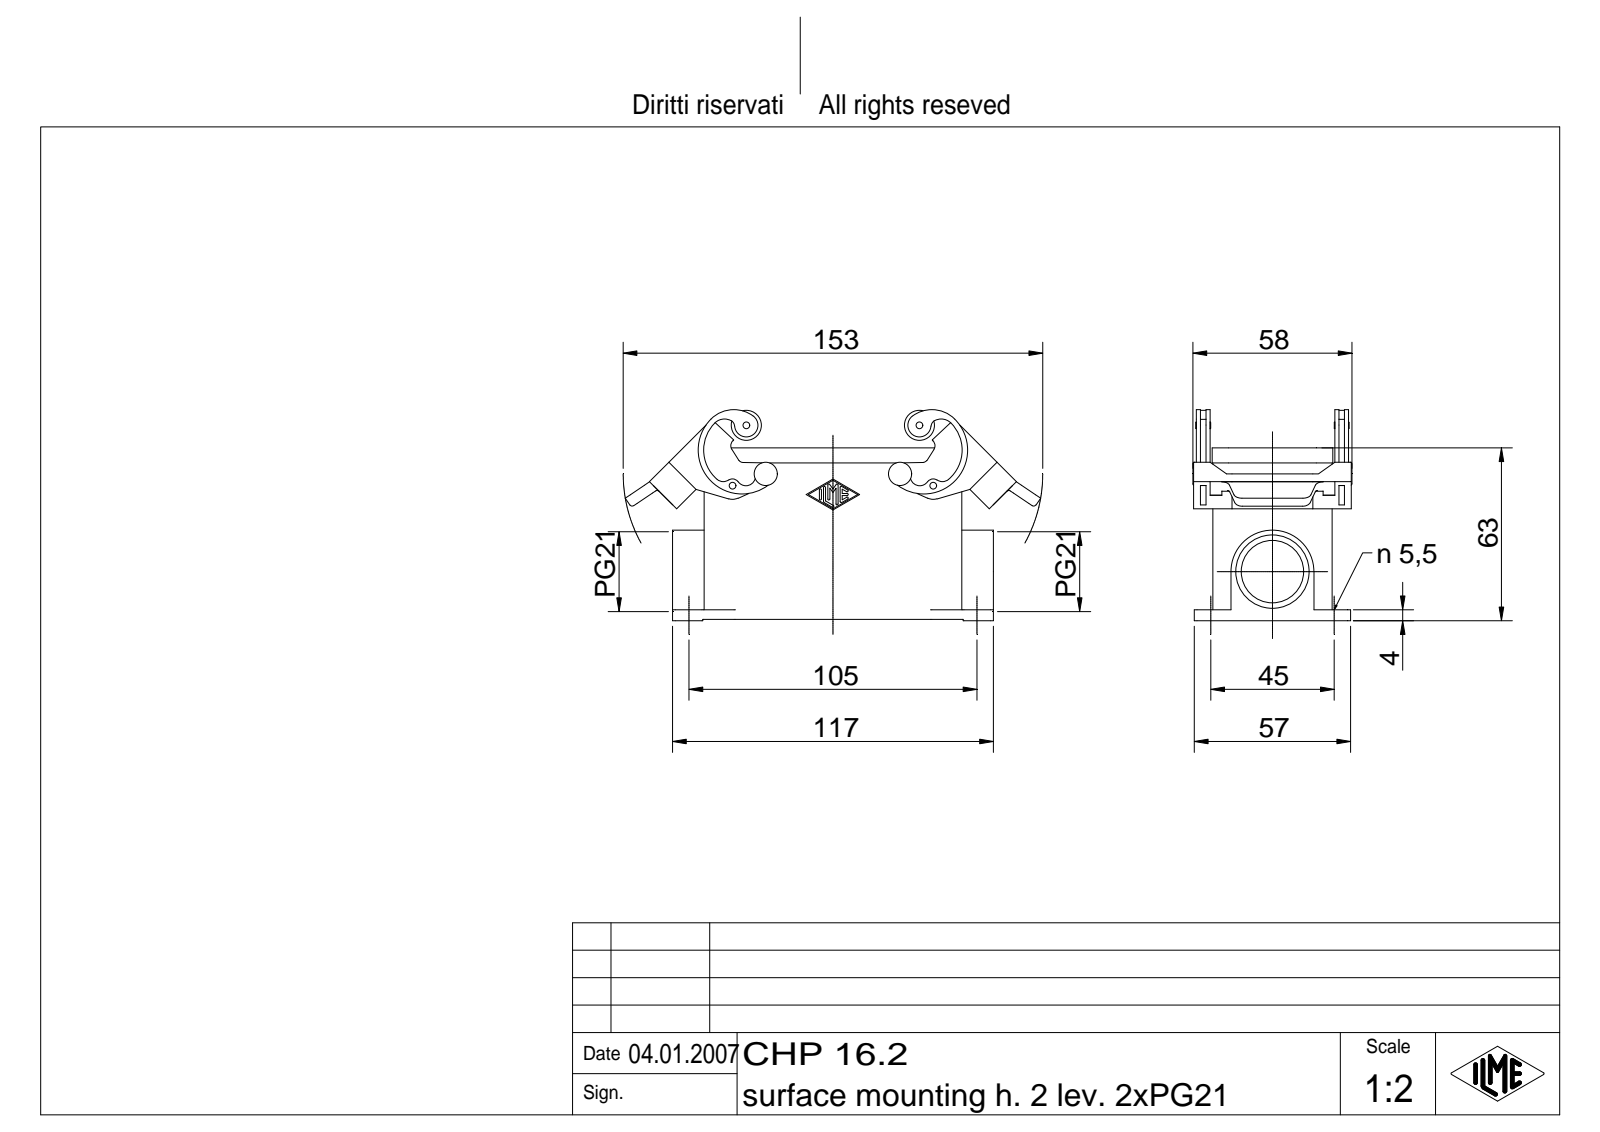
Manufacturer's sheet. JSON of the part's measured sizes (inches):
{"part_name": "CHP 16.2", "step_written_by": "Autodesk Inventor 7 (AUTOMOTIVE_DESIGN)", "units": "inches", "bodies": {"solids": 1, "faces": 748, "planar": 191, "cylindrical": 205, "other": 352}, "overall_size": [5.964, 3.029, 2.283], "volume_in3": 6.405, "surface_area_in2": 95.6, "round_holes": [[0.079, 4], [0.217, 4], [0.098, 2], [0.897, 1], [1.054, 1]], "round_bosses_or_shafts": [[0.433, 2], [0.197, 2], [0.118, 2]], "partial_cylinders_radius": [[0.039, 20], [0.015, 14], [0.118, 12], [0.236, 8], [0.098, 6], [0.059, 4], [0.079, 4], [0.138, 4]], "face_to_face_distances": [0.118, 1.594, 1.713, 0.138, 1.476, 0.157, 1.988, 0.03, 1.604, 0.177], "hole_center_spacings": [0.888, 1.772, 2.82, 4.134, 4.498, 2.486, 2.881]}
